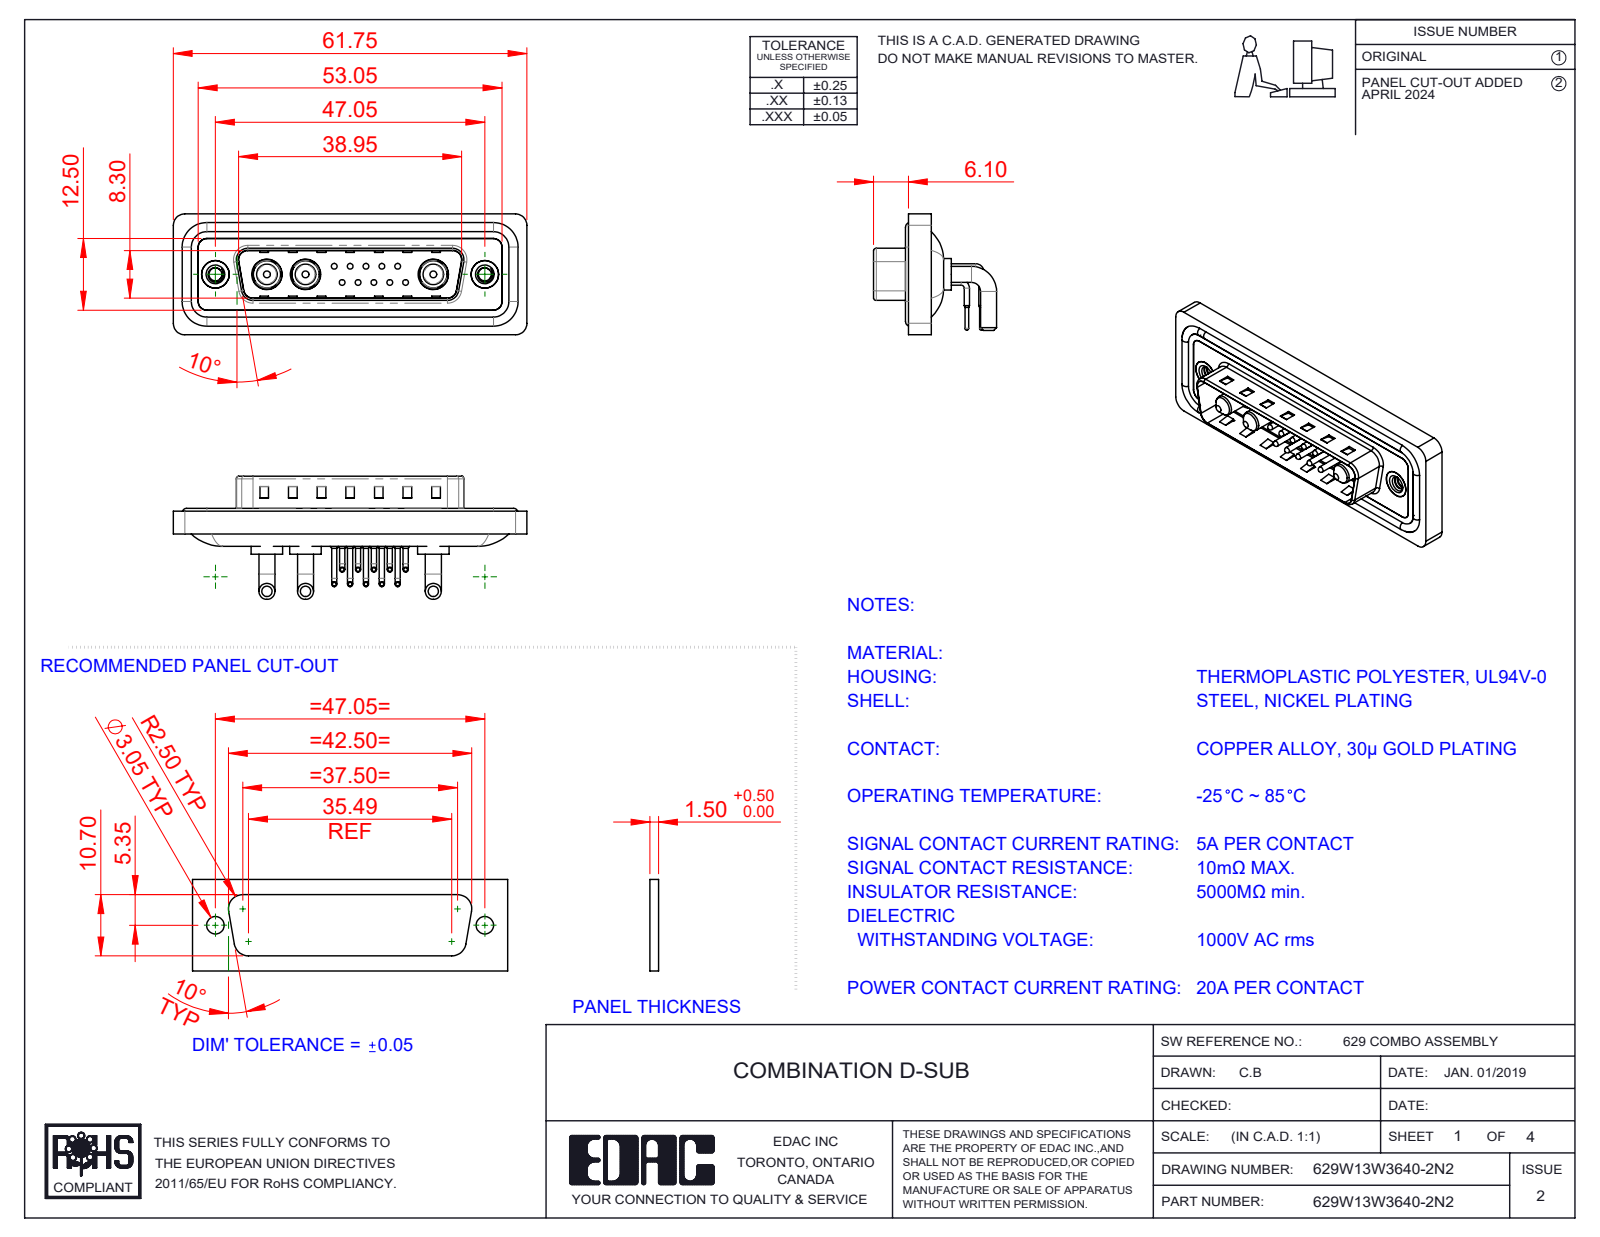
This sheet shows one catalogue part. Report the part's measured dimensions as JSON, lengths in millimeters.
{"part_name": "629Combo Housing_13W3; 629Combo Contact Row 2; 629Combo Shell Rear_25 Contacts; 629W13W3640-2N2 (+5 more)", "step_written_by": "SolidWorks 2023 (CONFIG_CONTROL_DESIGN)", "units": "millimeters", "bodies": {"solids": 23, "faces": 1712, "planar": 879, "cylindrical": 611, "other": 222}, "overall_size": [61.75, 21.5, 21.1], "volume_mm3": 7621, "surface_area_mm2": 12497, "round_holes": [[0.75, 10], [1.6, 10], [2, 10], [4.85, 3], [5.3, 3], [2.26, 2], [4, 2], [4.8, 2], [5, 2]], "round_bosses_or_shafts": [[0.9, 20], [1.5, 10], [1, 10], [0.65, 10], [2.8, 6], [1.6, 4], [5.5, 3], [5.2, 3]], "partial_cylinders_radius": [[1.5, 18], [2, 18], [1.01, 10], [0.5, 8], [1.6, 8], [0.25, 4], [0.6, 4], [0.65, 4]], "face_to_face_distances": [0.4, 2.9, 0.8, 4.1, 1.1, 2.1, 1.6, 4.5, 1.5, 2.5], "hole_center_spacings": [3.16, 2.77, 5.04, 5.54, 7.49, 5.03, 8.31, 10.11]}
